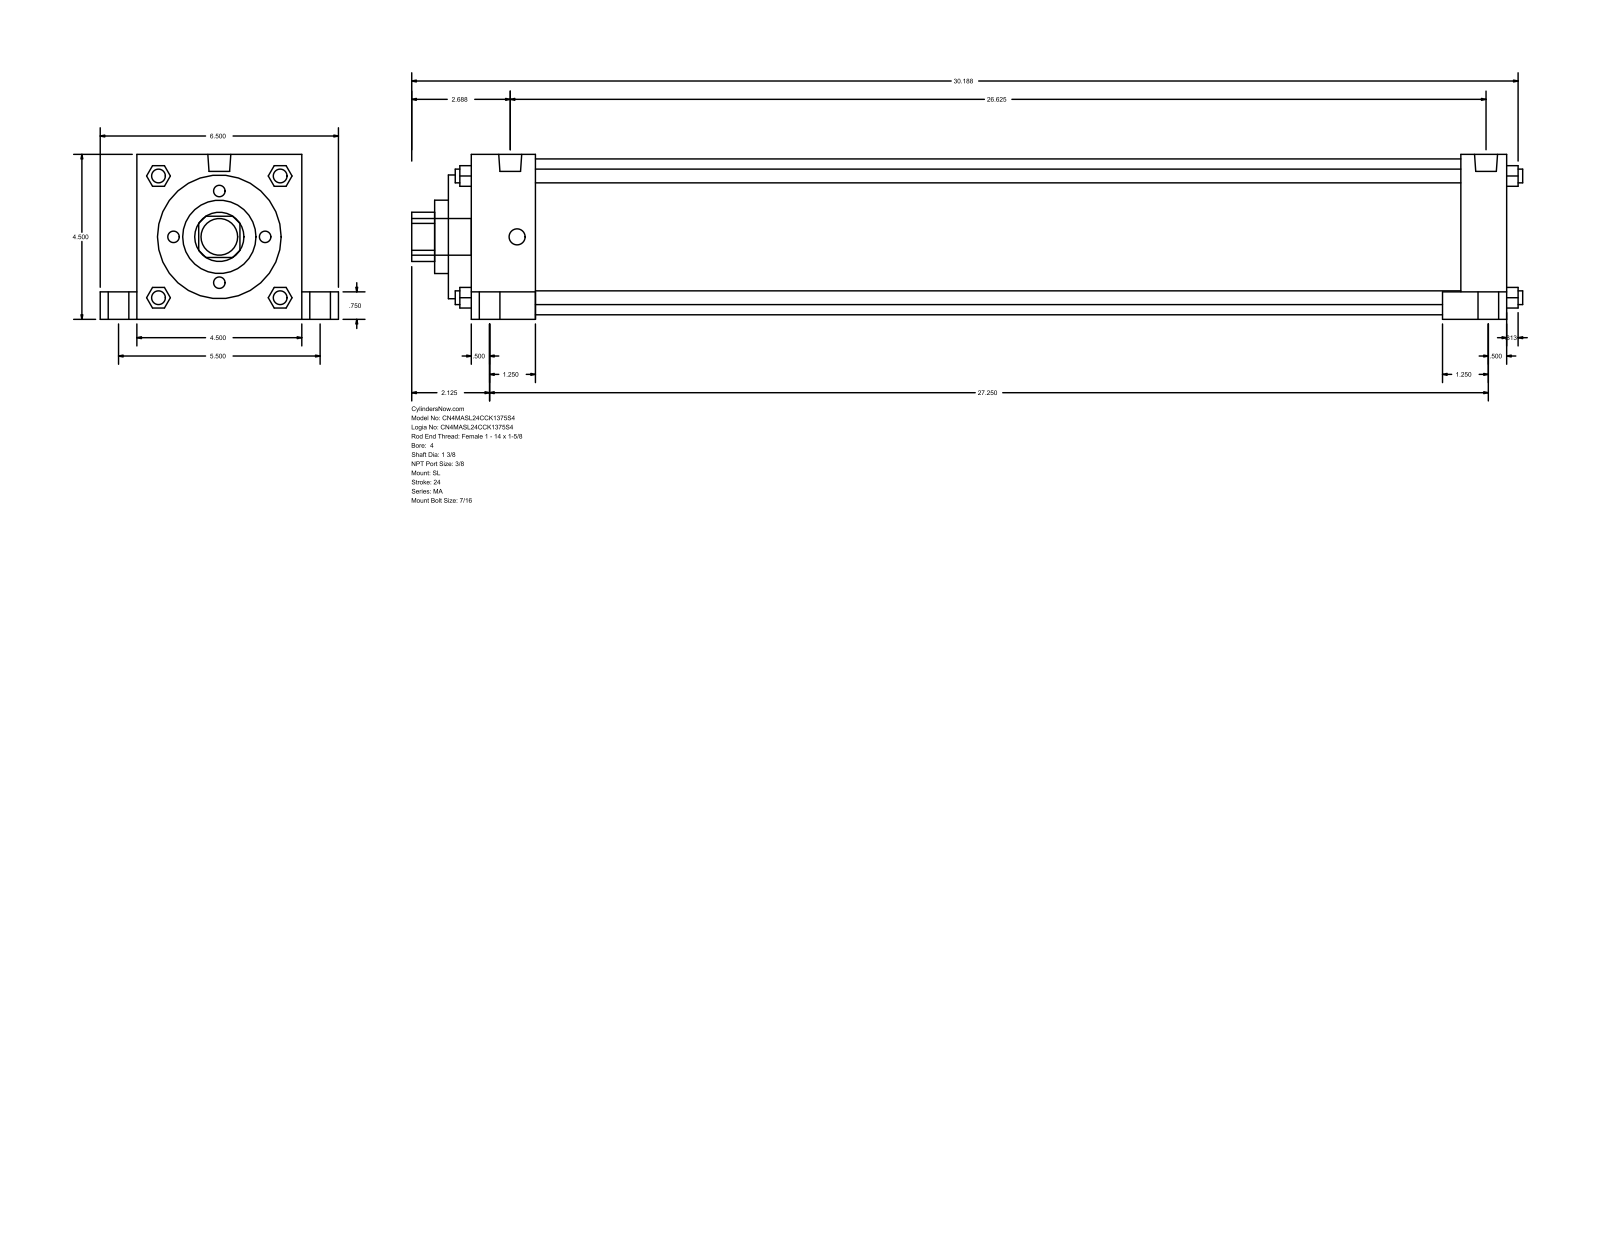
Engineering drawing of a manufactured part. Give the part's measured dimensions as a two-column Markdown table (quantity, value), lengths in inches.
| quantity | value |
| --- | --- |
| part name | MA_SL__0400_1.375 |
| STEP written by | GSSL Pune (CONFIG_CONTROL_DESIGN) |
| units | inches |
| bodies | 0 solids, 150 faces (113 planar, 37 cylindrical, 0 other) |
| overall size | 30.313 × 6.5 × 4.5 |
| round holes (diameter × count) | 1.375 × 1, 2 × 1, 3.375 × 1, 4.25 × 1 |
| round bosses / shafts (diameter × count) | 0.813 × 4, 0.563 × 4, 0.437 × 4, 0.375 × 4, 0.627 × 2, 1 × 1 |
| partial cylindrical surfaces (radius × count) | 0.672 × 1 |
| main face-to-face distances | 4.5, 28.25, 0.625, 28.875, 2.375, 1.75, 26.5, 27.625, 27, 25.25 |
